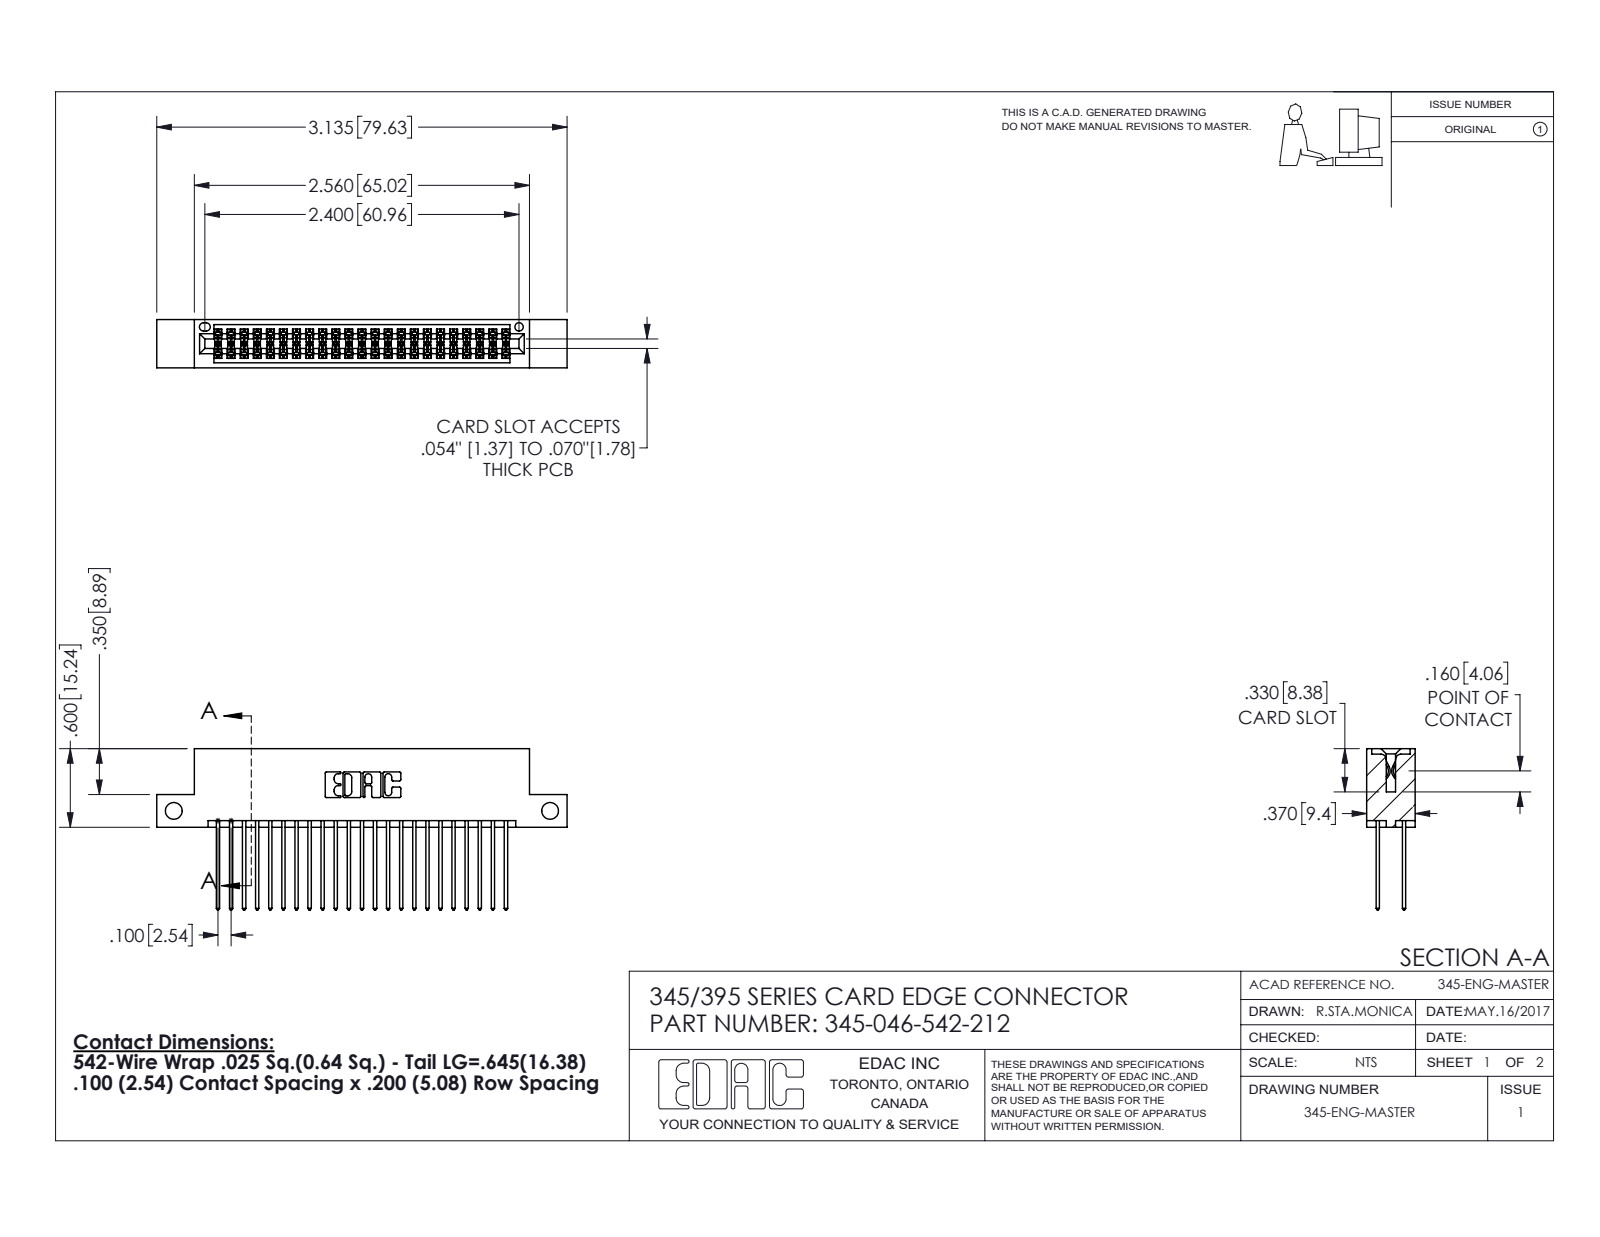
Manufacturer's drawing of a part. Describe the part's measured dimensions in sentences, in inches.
The part is named "345 Part_Flush Mounting Lugs - Side Mount; 345-046-542-212; 345-292-001_345-293-142". Its 3-D file was written by "SolidWorks 2016 (CONFIG_CONTROL_DESIGN)". It is 47 solids with 2426 faces: 1598 planar, 828 cylindrical and 0 other. Overall it measures 3.135 by 1.232 by 0.37 inches. Its volume is 0.469 cubic inches and its surface area 18.38 square inches. Round holes: 2 of diameter 0.128, 1 of diameter 0.064. Partial cylindrical surfaces (rounded edges, fillets, slot ends): 69 of radius 0.006, 46 of radius 0.01, 22 of radius 0.01, 6 of radius 0.007, 6 of radius 0.031, 3 of radius 0.026, 2 of radius 0.014, 2 of radius 0.019. The main face-to-face distances are 0.298, 0.072, 0.2, 0.098, 0.272, 0.025, 0.37, 0.225, 0.175, 0.149. The hole center spacings are 2.875.
